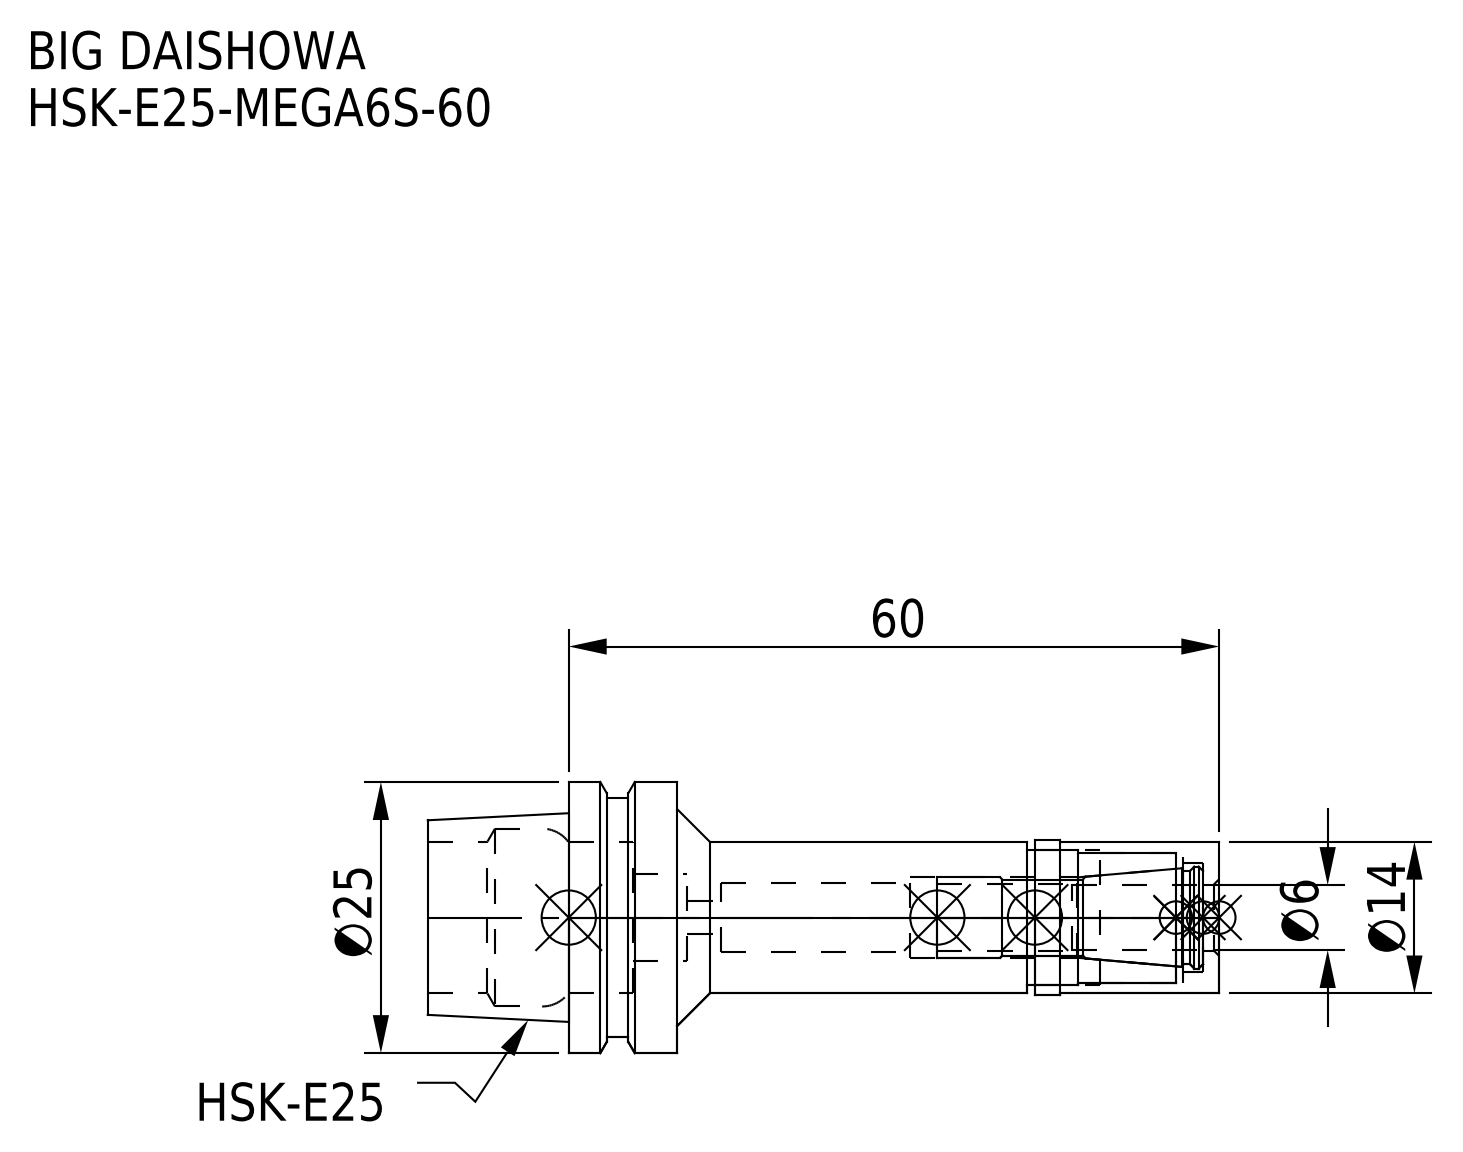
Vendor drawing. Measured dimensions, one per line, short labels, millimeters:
name: HSK-E25-MEGA6S-60-060.stp; HSK-E25-MEGA6S-60; HSK-E25-MEGA6S-60_1.stp; HE25MS06060-060_ASM.stp (+3 more)
written by: SolidWorks 2019 (CONFIG_CONTROL_DESIGN)
unit: mm
bodies: 2 solids, 74 faces (18 planar, 40 cylindrical, 16 other)
size: 73 × 25 × 25
volume: 10 544 mm³; area: 8 119 mm²
holes: 1× ⌀3, 1× ⌀6.1, 1× ⌀6.4, 1× ⌀7.4, 1× ⌀8, 1× ⌀10, 1× ⌀12, 1× ⌀12.5, 1× ⌀14, 1× ⌀16.4
bosses: 1× ⌀25, 1× ⌀22, 1× ⌀14.3
face distances: 10, 13, 60, 50, 54.05, 4.05, 5.95, 73, 23, 18.95
